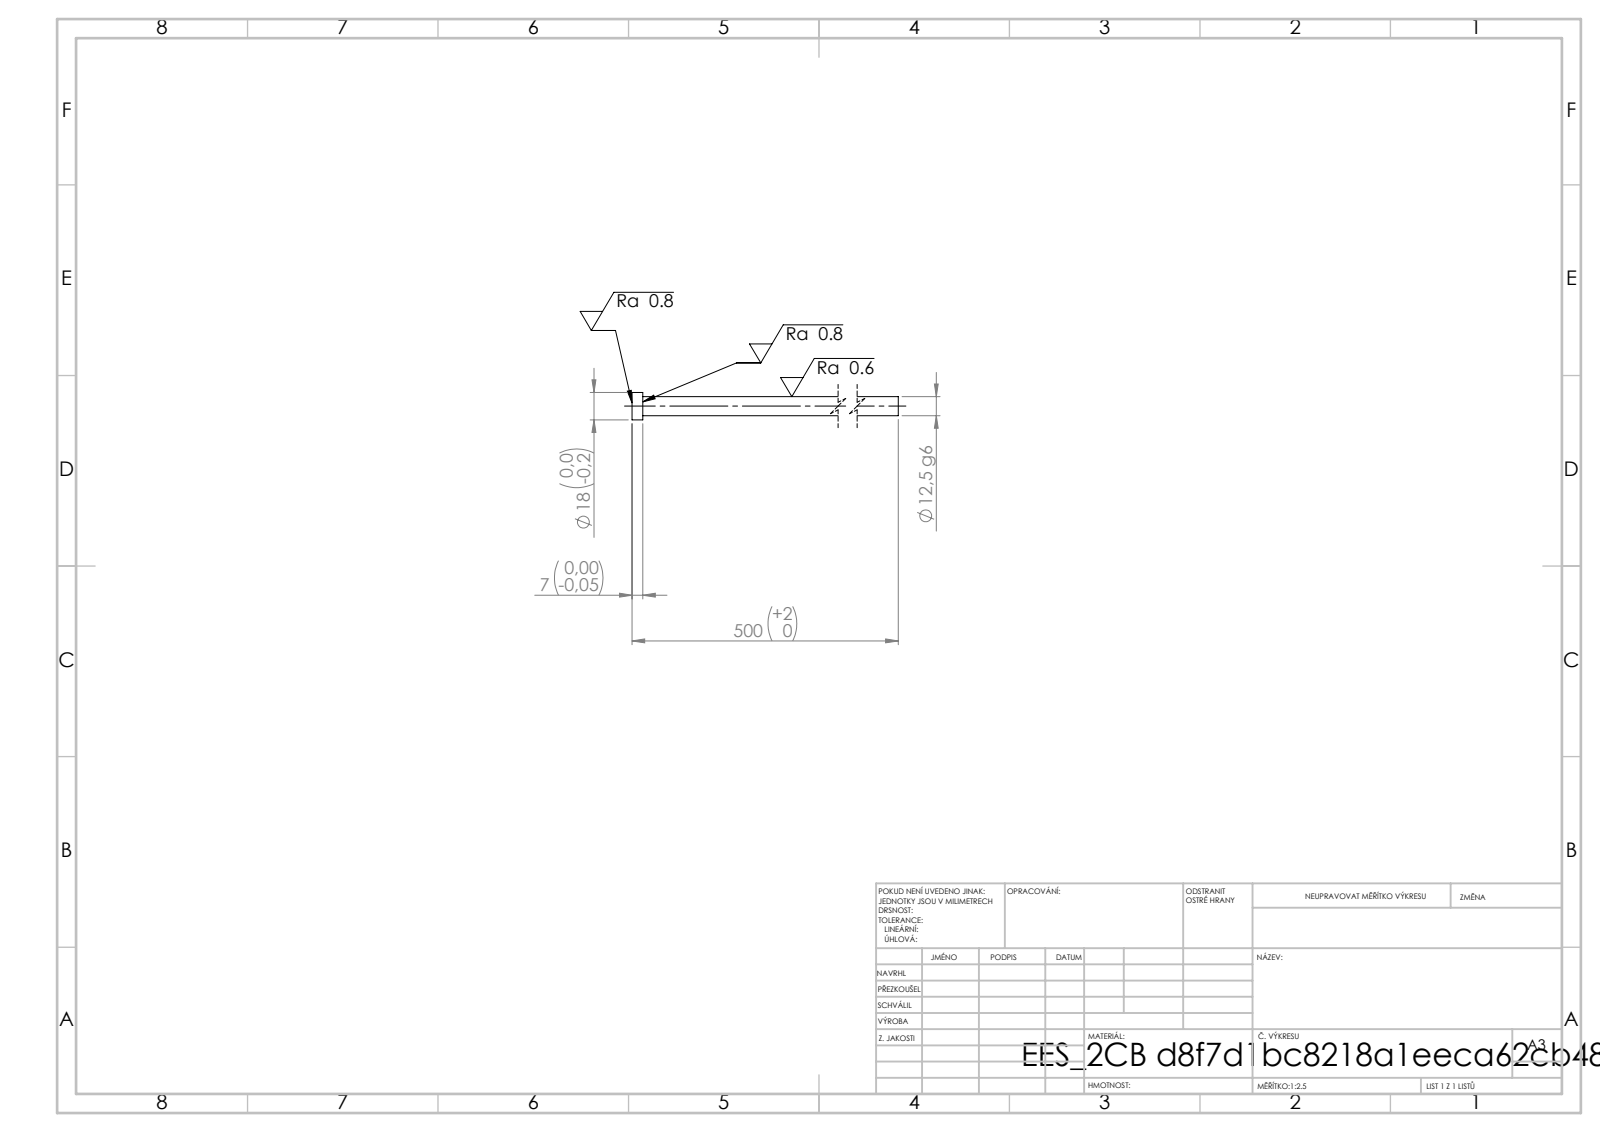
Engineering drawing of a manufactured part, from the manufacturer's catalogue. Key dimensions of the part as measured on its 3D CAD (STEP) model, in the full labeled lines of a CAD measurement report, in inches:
STEP written by: SolidWorks 2019 (CONFIG_CONTROL_DESIGN)
Units: inches
Bodies: 1 solid, 7 faces (3 planar, 4 cylindrical, 0 other)
Overall size (bounding box): 19.685 × 0.709 × 0.709
Volume: 3.801 in³ · Surface area: 31.41 in²
Round bosses / shafts (diameter × count): ⌀0.709 ×1, ⌀0.492 ×1
Main face-to-face distances: 0.276, 19.685, 19.409
